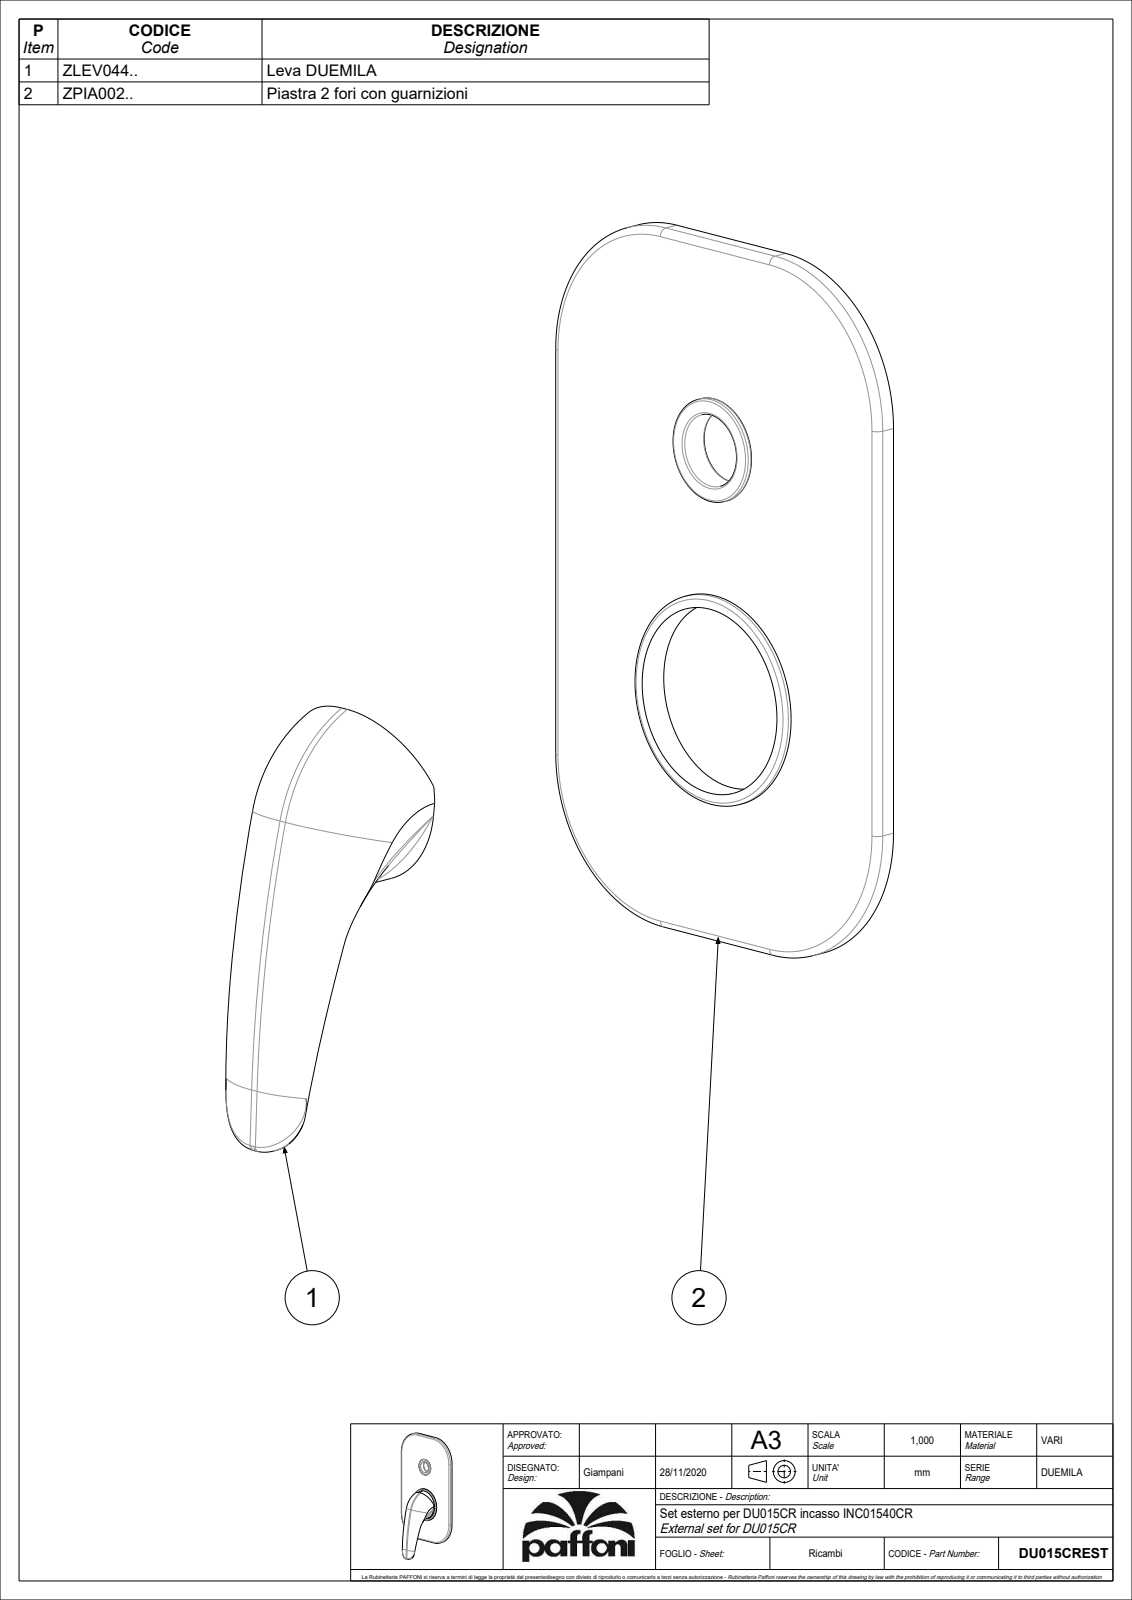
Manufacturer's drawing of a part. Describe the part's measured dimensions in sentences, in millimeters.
The part is named "DU015CREST". Its 3-D file was written by "CREO PARAMETRIC BY PTC INC, 2020044 (CONFIG_CONTROL_DESIGN)". It is 2 solids with 169 faces: 53 planar, 58 cylindrical and 58 other. Overall it measures 214.4 by 120.5 by 52.52 millimeters. Its volume is 57 510 cubic millimeters and its surface area 61 789 square millimeters. Round holes: 1 of diameter 6, 1 of diameter 7.8, 1 of diameter 9.2, 1 of diameter 19.1, 1 of diameter 50. Round bosses or shafts: 1 of diameter 56.5, 1 of diameter 55, 1 of diameter 25.1, 1 of diameter 23.5, 1 of diameter 18.1, 1 of diameter 8, 1 of diameter 5. Partial cylindrical surfaces (rounded edges, fillets, slot ends): 4 of radius 1.2, 4 of radius 2, 4 of radius 39.2, 4 of radius 40, 2 of radius 1.5, 2 of radius 15, 2 of radius 24, 2 of radius 24.5. The main face-to-face distances are 0.8, 5.2, 119.7, 6, 118.9, 2, 120.5, 8, 2.8, 189.2. The hole center spacings are 68.
